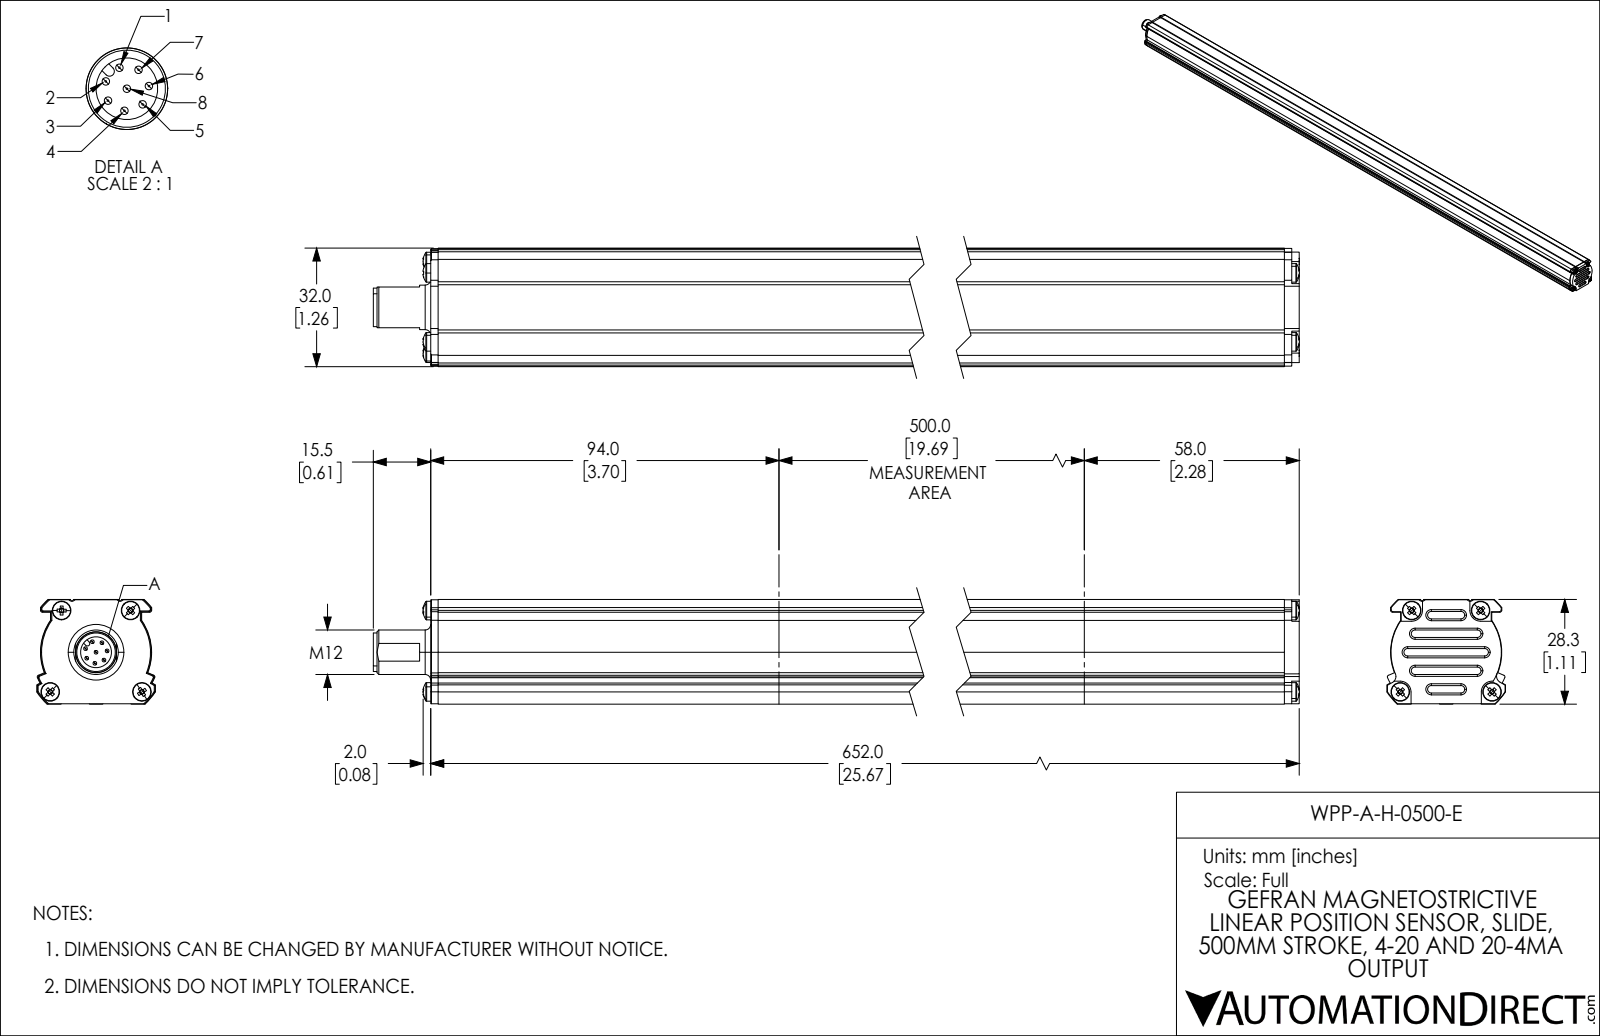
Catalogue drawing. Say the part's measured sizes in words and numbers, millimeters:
The part is named "WPP-A-H-0500-E". Its 3-D file was written by "SolidWorks 2021 (CONFIG_CONTROL_DESIGN)". It is 20 solids with 605 faces: 301 planar, 131 cylindrical and 173 other. Overall it measures 667.55 by 32 by 28.25 millimeters. Its volume is 520 030 cubic millimeters and its surface area 107 092 square millimeters. Round holes: 5 of diameter 2.6, 4 of diameter 2.3, 1 of diameter 7, 1 of diameter 8.3, 1 of diameter 9.4. Round bosses or shafts: 8 of diameter 1, 4 of diameter 5, 1 of diameter 12, 1 of diameter 10.4, 1 of diameter 9.55, 1 of diameter 8. Partial cylindrical surfaces (rounded edges, fillets, slot ends): 8 of radius 0.5, 4 of radius 2.9, 2 of radius 0.4, 2 of radius 1, 2 of radius 1.85, 1 of radius 0.65, 1 of radius 2, 1 of radius 14.9. The main face-to-face distances are 28, 28.25, 24.8, 24.55, 3.45, 3.7, 28.3, 646, 24.6, 32. The hole center spacings are 16.36, 14.6, 22.17, 30.85, 18.6, 22.16, 24.75, 24.76.
